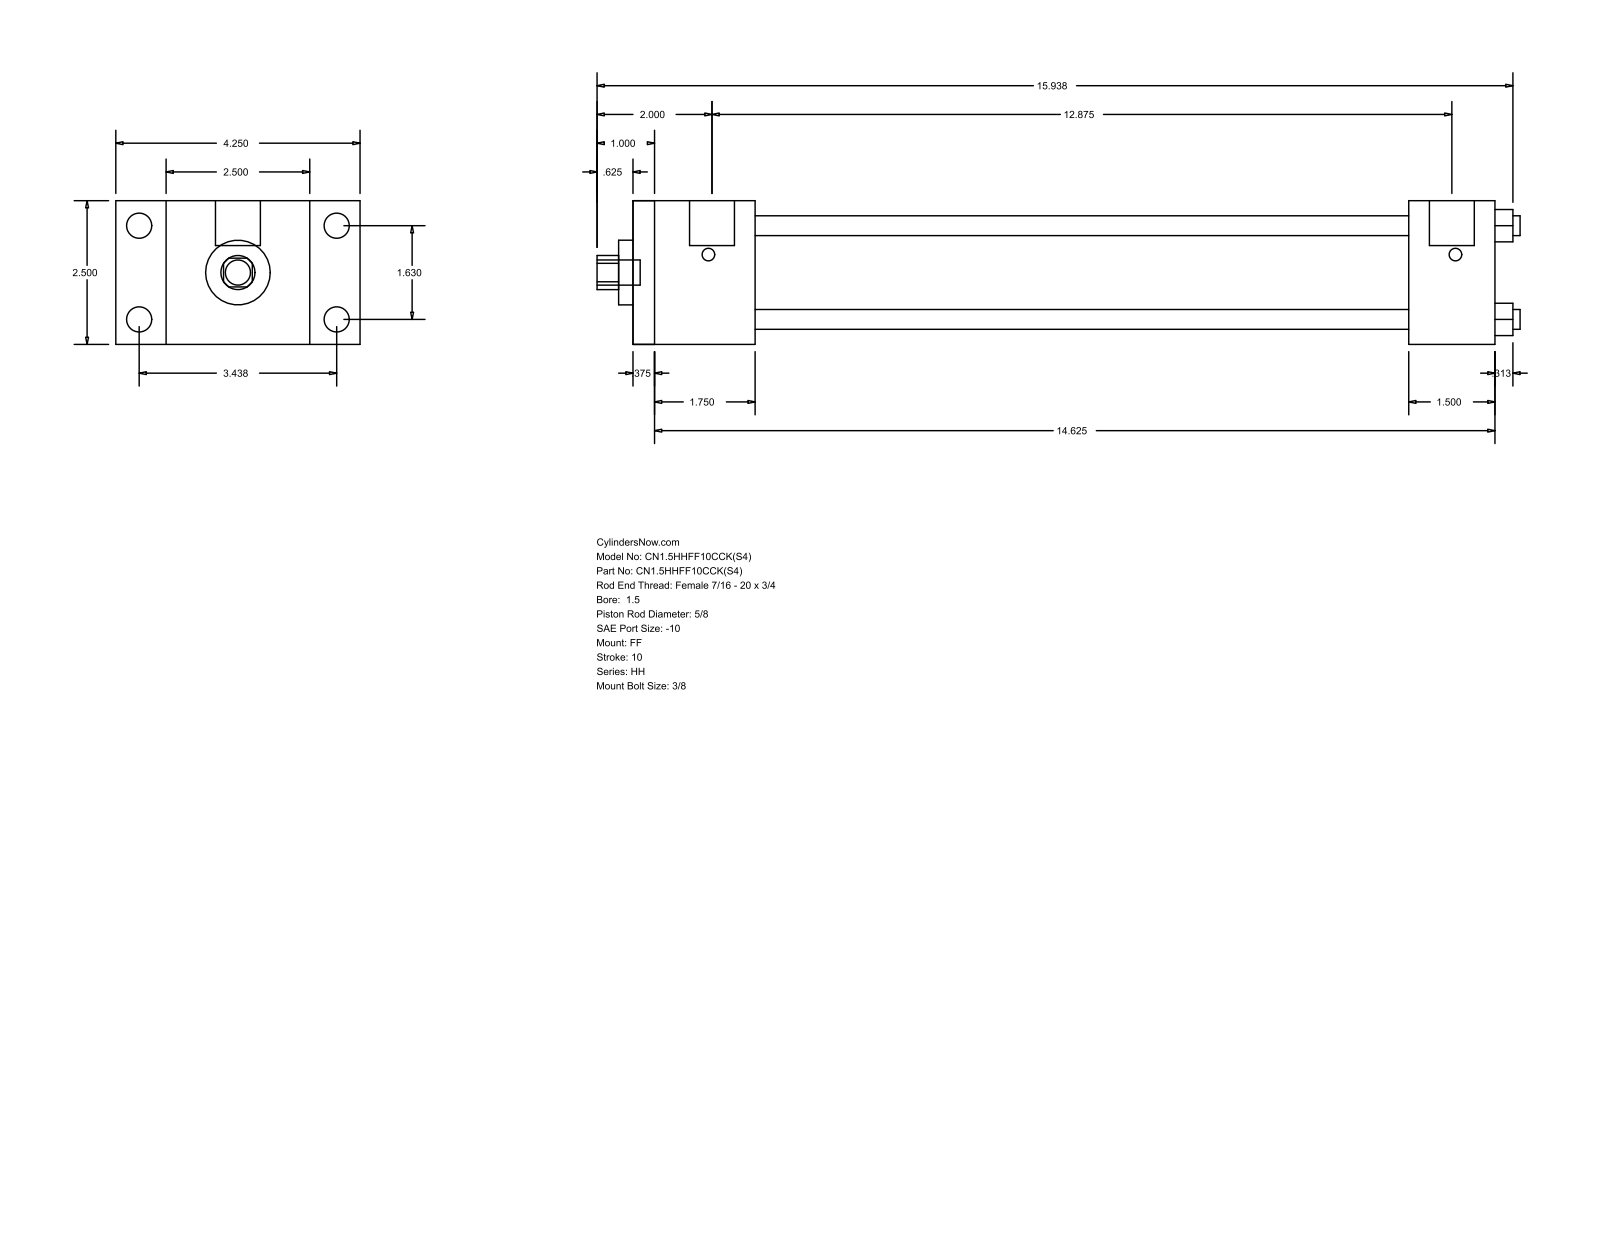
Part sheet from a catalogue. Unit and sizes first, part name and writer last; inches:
Units: inches
Overall size (bounding box): 16.063 × 4.25 × 2.5
Round holes (diameter × count): ⌀0.345 ×4, ⌀0.625 ×1, ⌀1.125 ×1, ⌀1.75 ×1
Round bosses / shafts (diameter × count): ⌀0.438 ×4, ⌀0.219 ×4, ⌀0.781 ×2, ⌀0.437 ×1
Partial cylindrical surfaces — rounded edges, fillets, slot ends (radius × count): R0.297 ×1
Main face-to-face distances: 2.5, 15, 0.375, 14.625, 2.125, 1.75, 12.875, 13.5, 13.125, 11.375
Hole centre spacings: 1.152, 1.63, 2.305
Bodies: 0 solids, 92 faces (64 planar, 28 cylindrical, 0 other)
Part name (STEP PRODUCT): HH_FF__0150_0.625
STEP written by: GSSL Pune (CONFIG_CONTROL_DESIGN)
